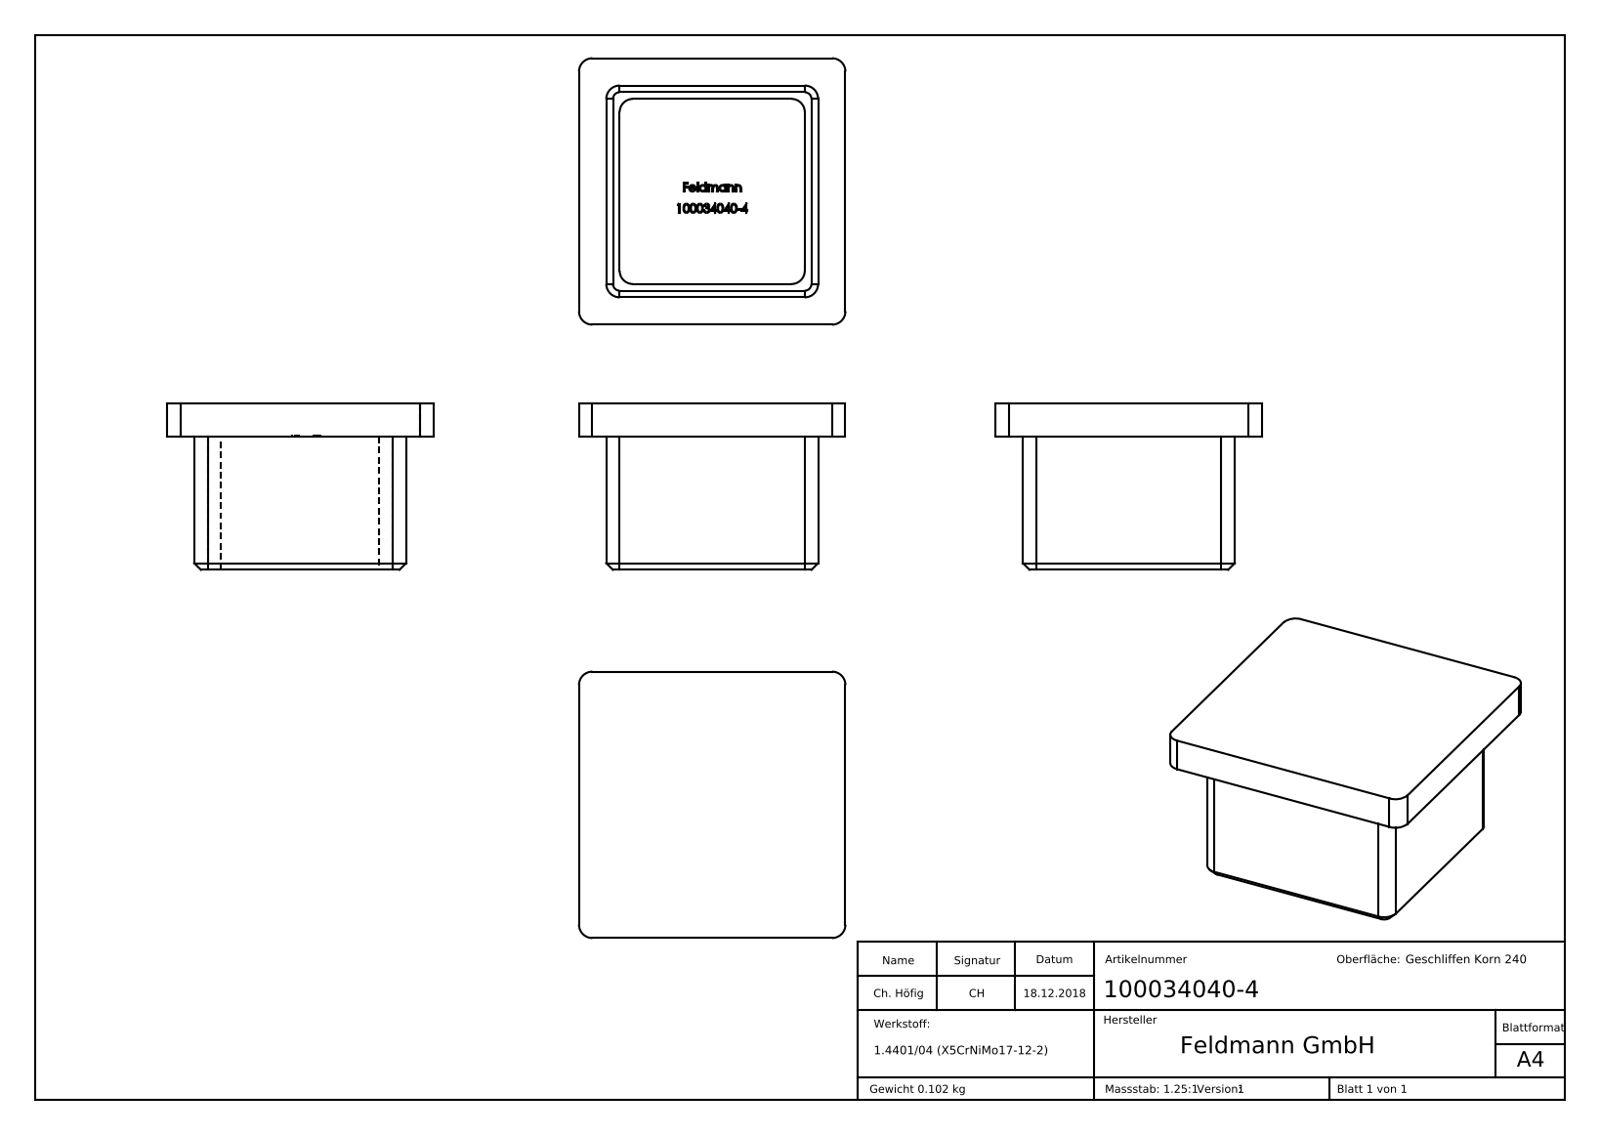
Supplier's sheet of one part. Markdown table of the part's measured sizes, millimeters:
| quantity | value |
| --- | --- |
| part name | 100034040-4 |
| STEP written by | SolidWorks 2015 (CONFIG_CONTROL_DESIGN) |
| units | millimeters |
| bodies | 1 solid, 279 faces (156 planar, 12 cylindrical, 111 other) |
| overall size | 40 × 40 × 25 |
| volume | 12 689 mm³ |
| surface area | 8 544 mm² |
| partial cylindrical surfaces (radius × count) | 2 × 12 |
| main face-to-face distances | 2, 29.8, 5, 31.8, 27.8, 4.1, 6.1, 33.9, 35.9, 40 |
